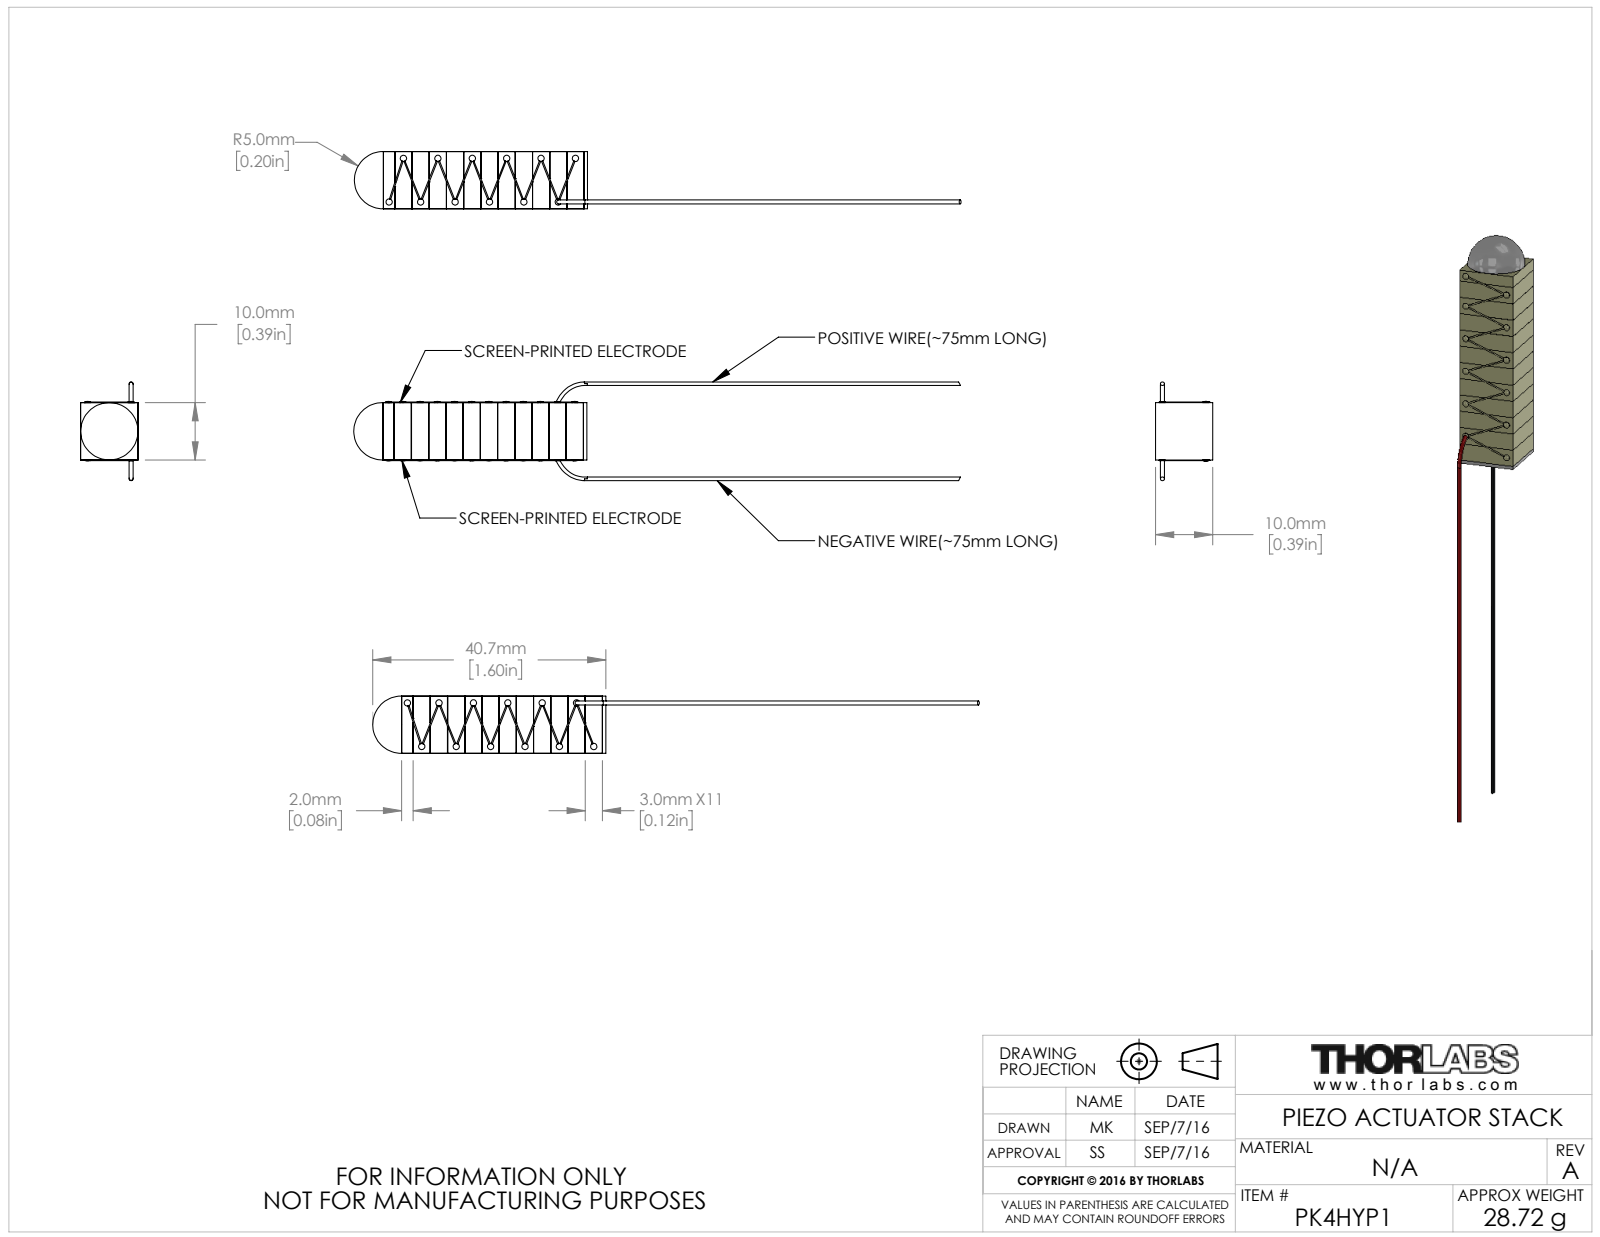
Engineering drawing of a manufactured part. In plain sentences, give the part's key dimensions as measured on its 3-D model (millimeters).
The part is named "CTN003318". Its 3-D file was written by "SolidWorks 2016 (AUTOMOTIVE_DESIGN)". It is 4 solids with 397 faces: 221 planar, 72 cylindrical and 104 other. Overall it measures 105.93 by 17.23 by 10 millimeters. Its volume is 7 382 cubic millimeters and its surface area 8 421 square millimeters. Round bosses or shafts: 12 of diameter 1.1. The main face-to-face distances are 3, 6, 3.01, 6.01, 10, 9.01, 12.01, 15.01, 18.01, 9.
